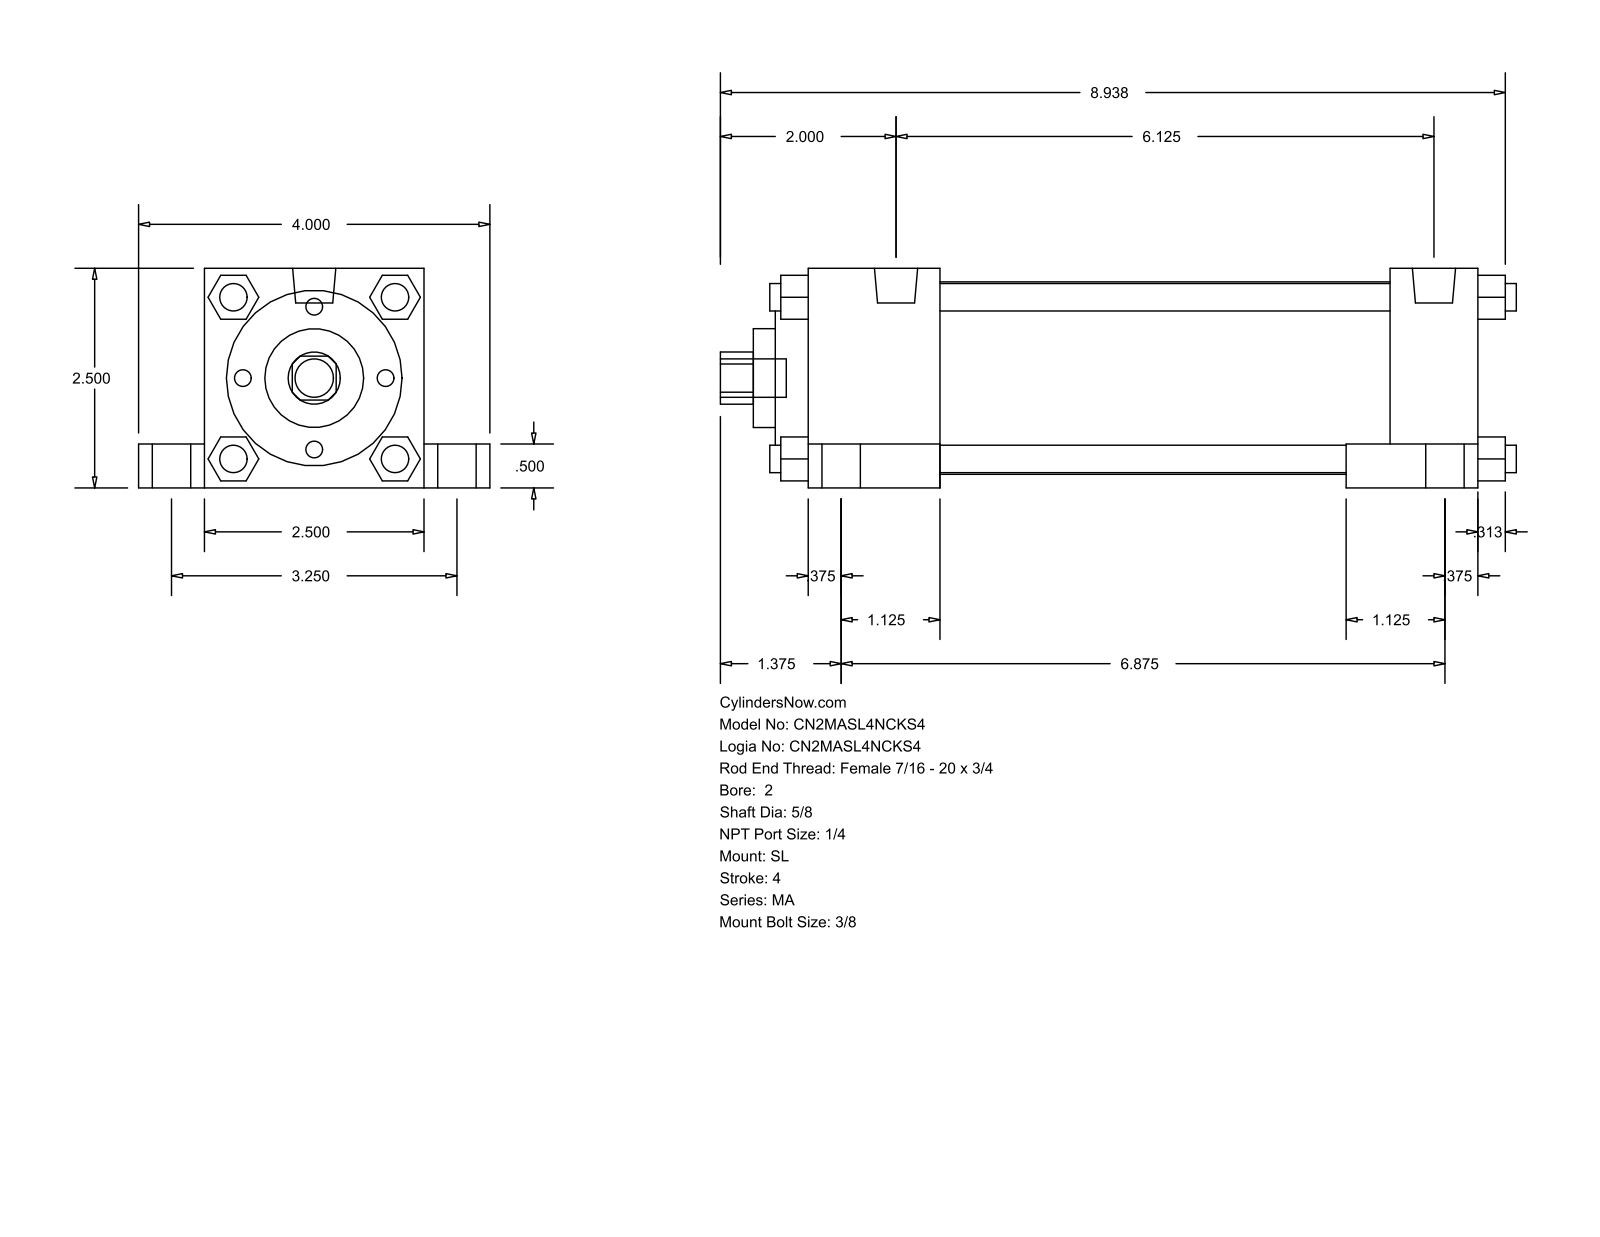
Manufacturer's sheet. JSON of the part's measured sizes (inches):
{"part_name": "MA_SL__0200_0.625", "step_written_by": "GSSL Pune (CONFIG_CONTROL_DESIGN)", "units": "inches", "bodies": {"solids": 0, "faces": 150, "planar": 113, "cylindrical": 37, "other": 0}, "overall_size": [9.063, 4, 2.5], "round_holes": [[0.625, 1], [1.125, 1], [2, 1], [2.19, 1]], "round_bosses_or_shafts": [[0.313, 8], [0.437, 5], [0.687, 4], [0.492, 2]], "partial_cylinders_radius": [[0.297, 1]], "face_to_face_distances": [2.5, 0.5, 0.375, 0.75, 3.25, 1.5, 2, 7.625, 6.125, 6.625]}
